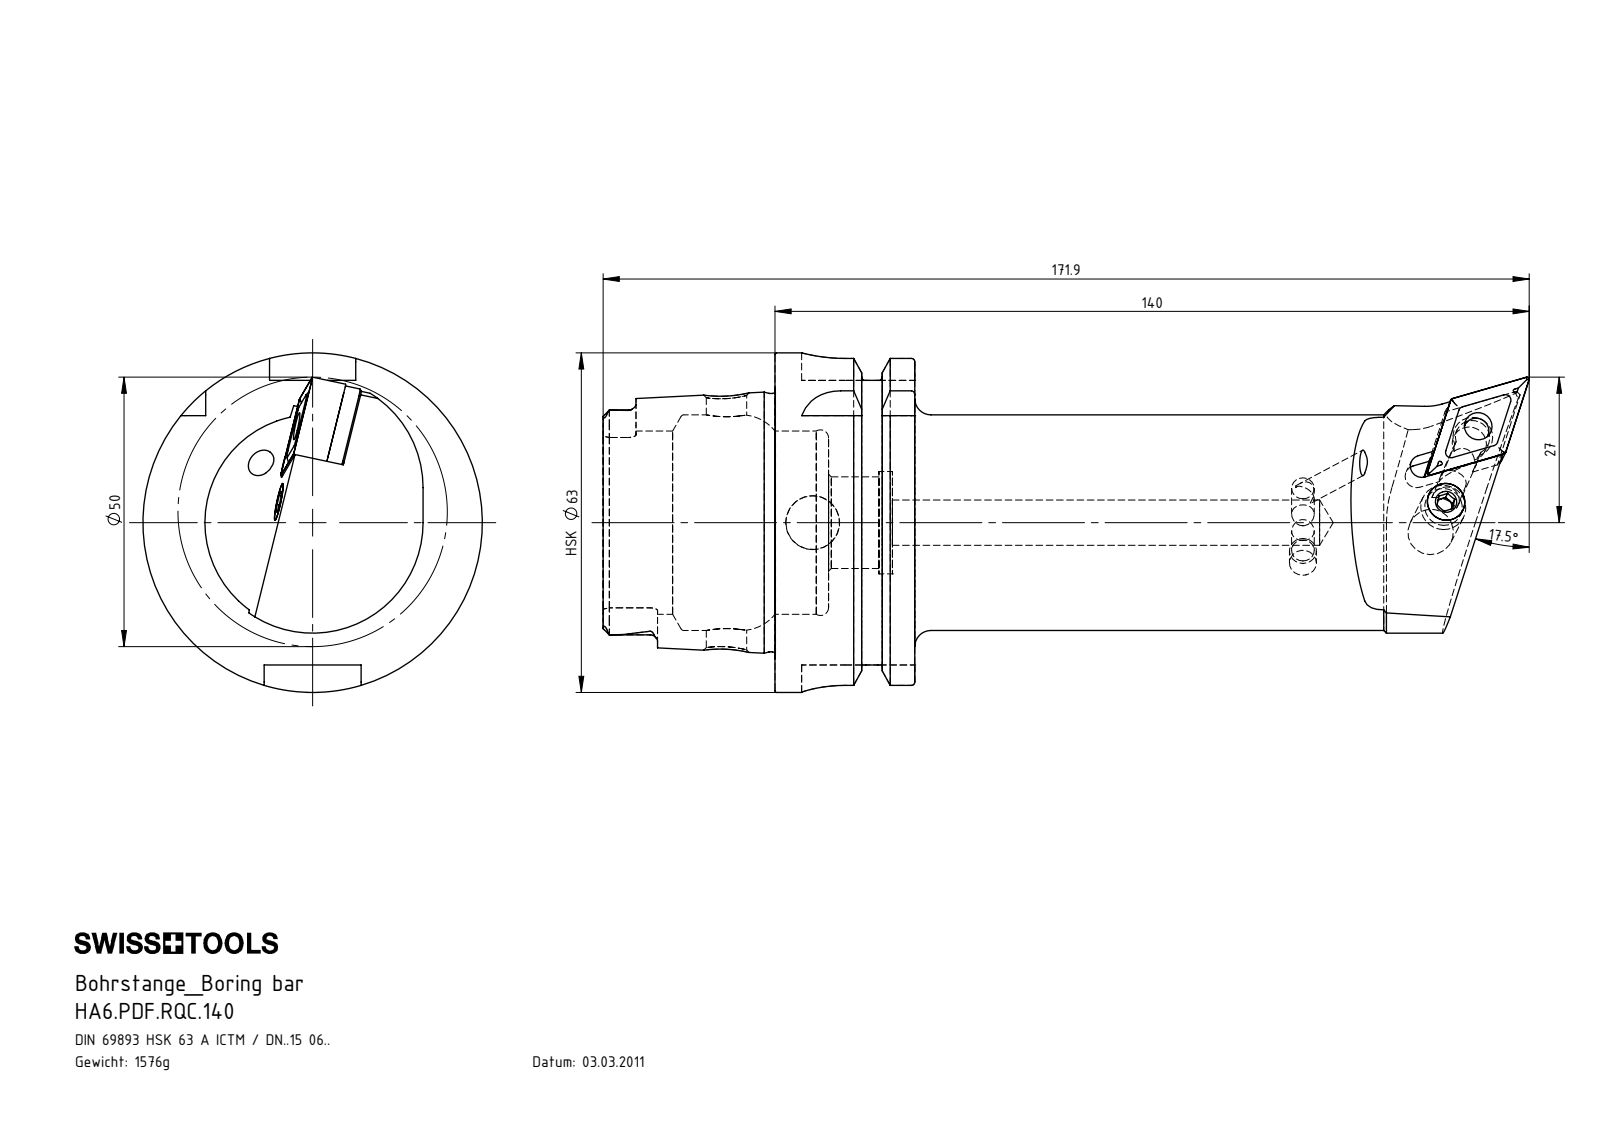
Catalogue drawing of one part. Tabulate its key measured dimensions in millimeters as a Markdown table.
| quantity | value |
| --- | --- |
| part name | HA6-PDF.RQC.140; DNMG150604; WDF-ER2.101.003_A; WCD-ER1.101.000 (+4 more) |
| STEP written by | SolidWorks 2012 (CONFIG_CONTROL_DESIGN) |
| units | millimeters |
| bodies | 8 solids, 368 faces (115 planar, 102 cylindrical, 151 other) |
| overall size | 171.9 × 63 × 63 |
| volume | 199 852 mm³ |
| surface area | 41 428 mm² |
| round holes (diameter × count) | 4.2 × 2, 8.4 × 2, 4 × 1, 5 × 1, 5.16 × 1, 6.4 × 1, 7 × 1, 7.5 × 1, 10 × 1, 17 × 1, 19 × 1, 34 × 1 |
| round bosses / shafts (diameter × count) | 63 × 1, 54.95 × 1, 47.94 × 1, 8 × 1, 7.9 × 1, 6.4 × 1, 5 × 1, 4.7 × 1 |
| partial cylindrical surfaces (radius × count) | 1.4 × 6, 0.4 × 4, 1 × 4, 8 × 4, 2.5 × 2, 2.82 × 2, 2.88 × 2, 2.1 × 1 |
| main face-to-face distances | 25.95, 16, 9.95, 6.04, 31.9, 41.85, 57.85, 52.8, 21.8, 11.85 |
| hole center spacings | 15.6 |
